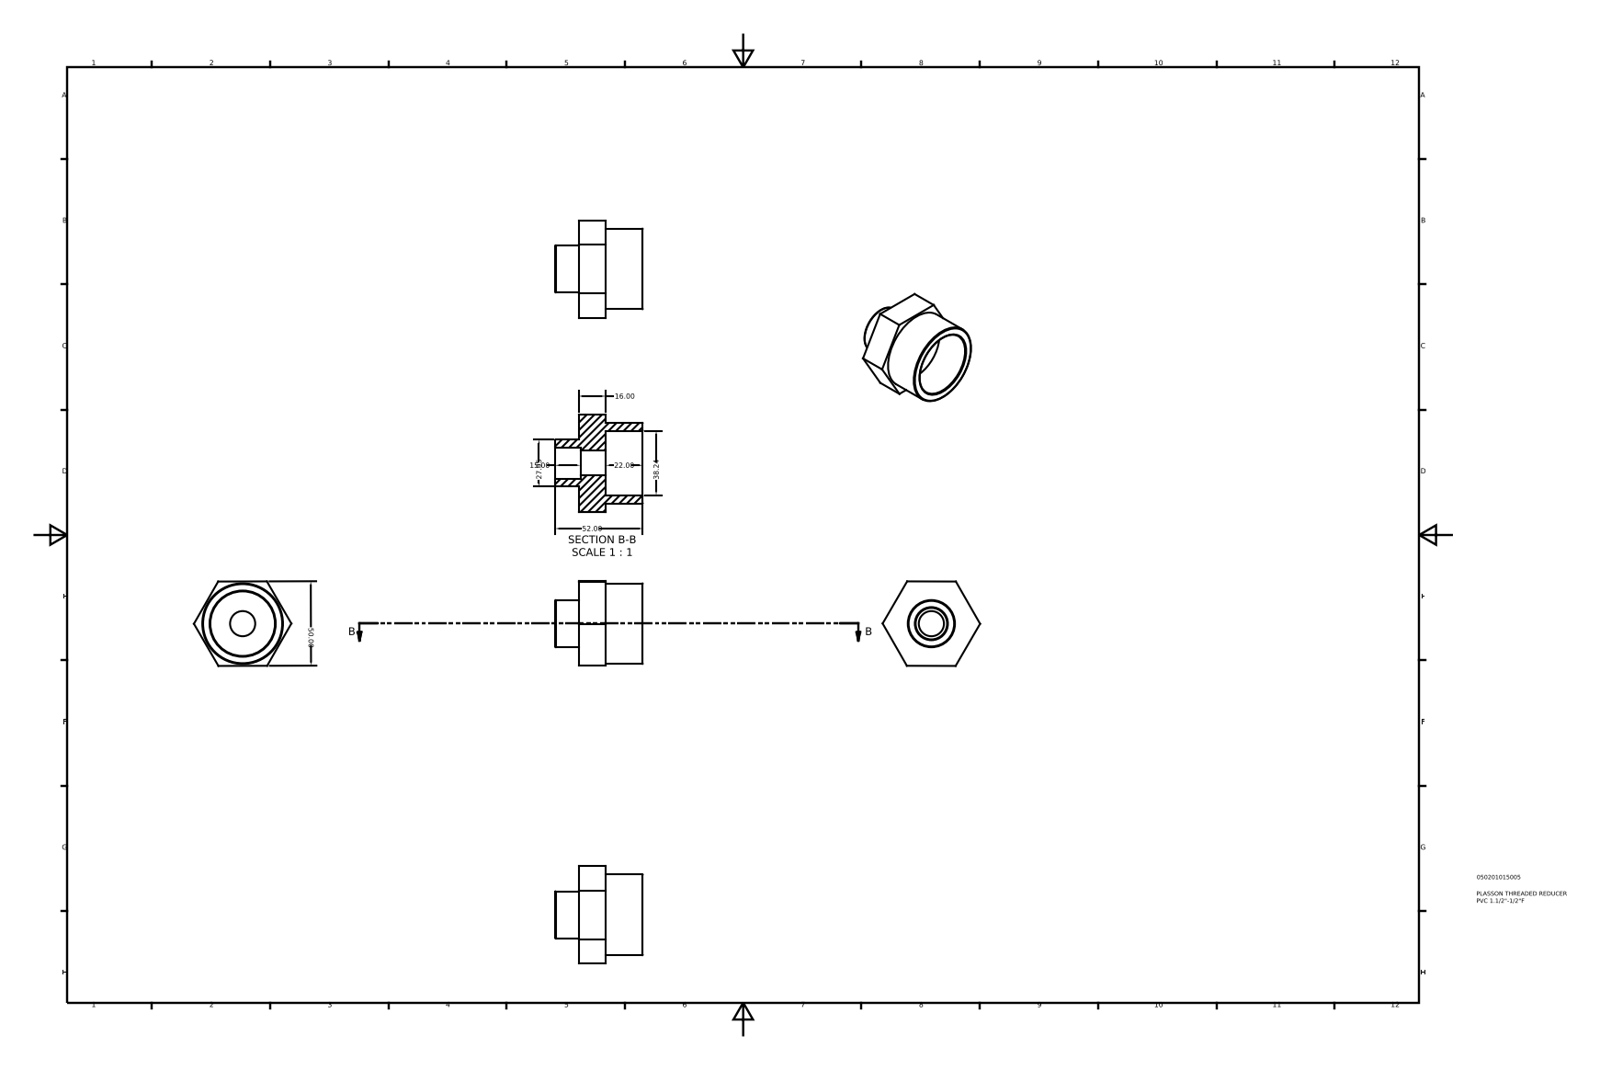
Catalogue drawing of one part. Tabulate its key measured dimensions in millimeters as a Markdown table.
| quantity | value |
| --- | --- |
| part name | 050201015005 |
| STEP written by | Autodesk Inventor 2015 (AUTOMOTIVE_DESIGN) |
| units | millimeters |
| bodies | 1 solid, 21 faces (12 planar, 5 cylindrical, 4 other) |
| overall size | 57.73 × 52 × 50.09 |
| volume | 50 716 mm³ |
| surface area | 15 423 mm² |
| round holes (diameter × count) | 14.9 × 1, 18.63 × 1, 38.24 × 1 |
| round bosses / shafts (diameter × count) | 47.8 × 1, 27.95 × 1 |
| main face-to-face distances | 16, 38, 22, 50.02, 50.04, 50, 14, 30, 52, 15 |
